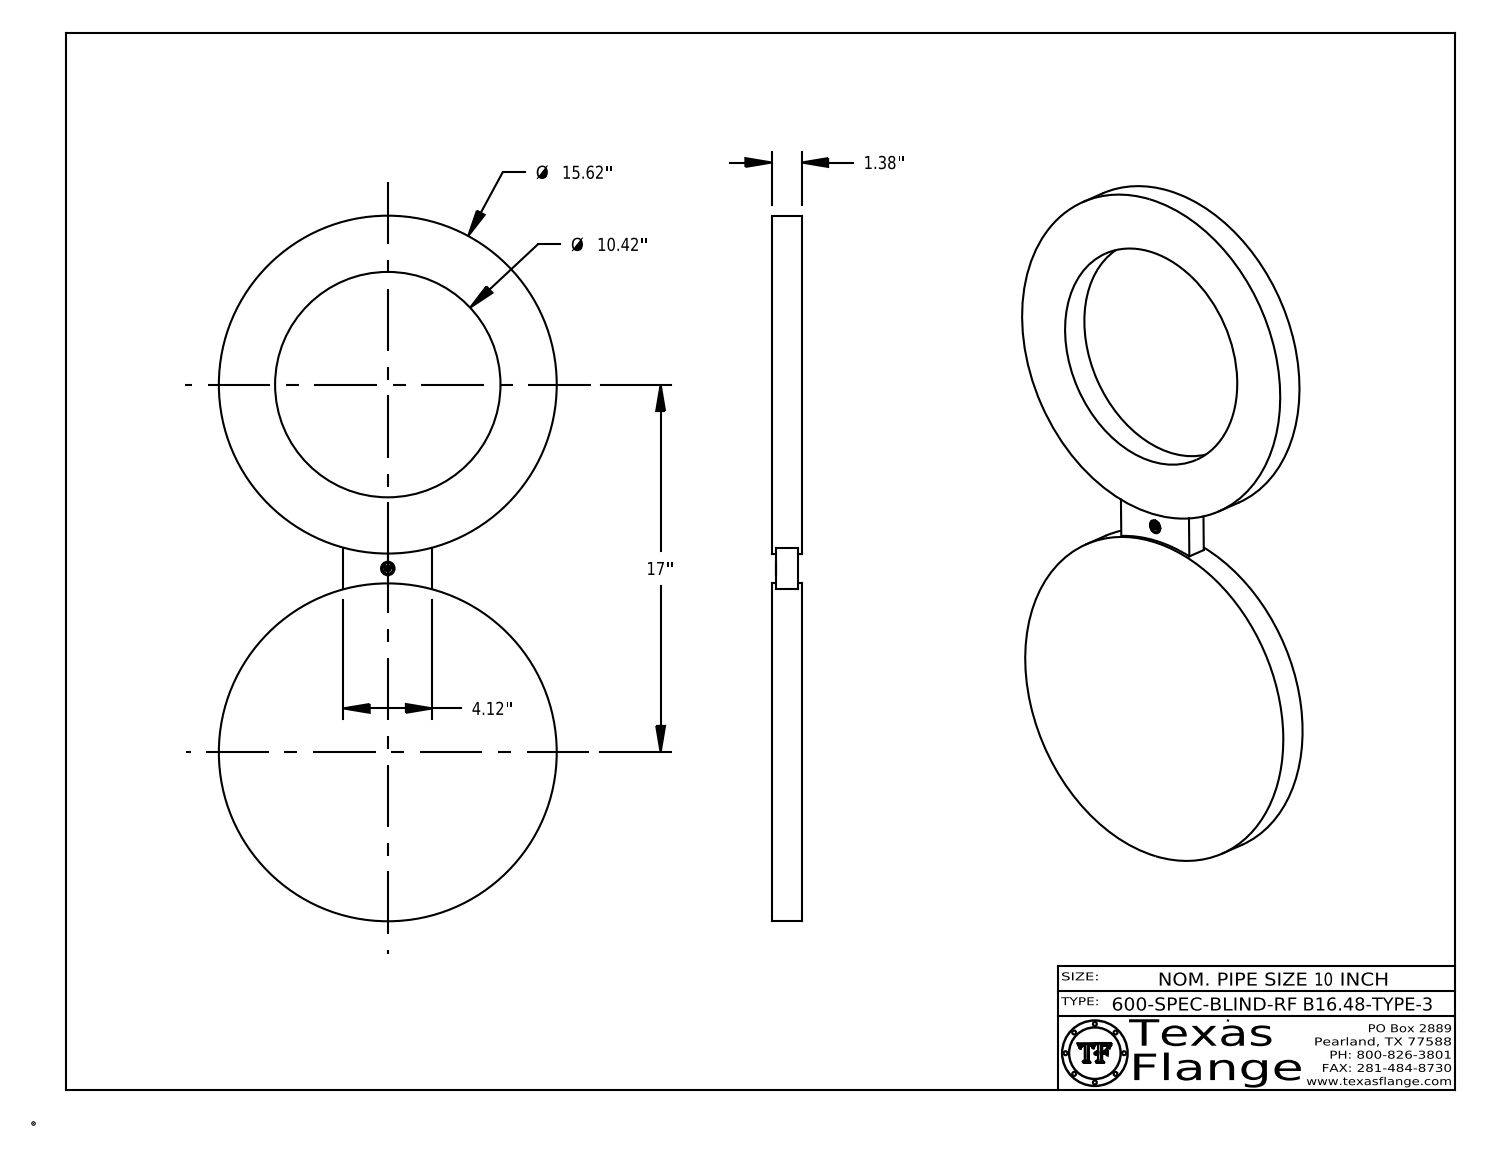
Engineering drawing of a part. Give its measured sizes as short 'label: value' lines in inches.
name: 10-600-SPEC-BLIND-RF-B16.48-TYPE-3
written by: CATIA V5 STEP AP214 (AUTOMOTIVE_DESIGN)
unit: in
bodies: 1 solid, 399 faces (373 planar, 26 cylindrical, 0 other)
size: 32.62 × 15.62 × 1.38
volume: 417.9 in³; area: 784.9 in²
holes: 1× ⌀0.625, 1× ⌀10.42
bosses: 8× ⌀0.038, 2× ⌀15.62, 1× ⌀0.492
face distances: 1.38, 0.173, 1.207, 1.035, 4.12, 1.193, 1.02, 0.015, 0.188, 1.997
hole spacings: 8.5
